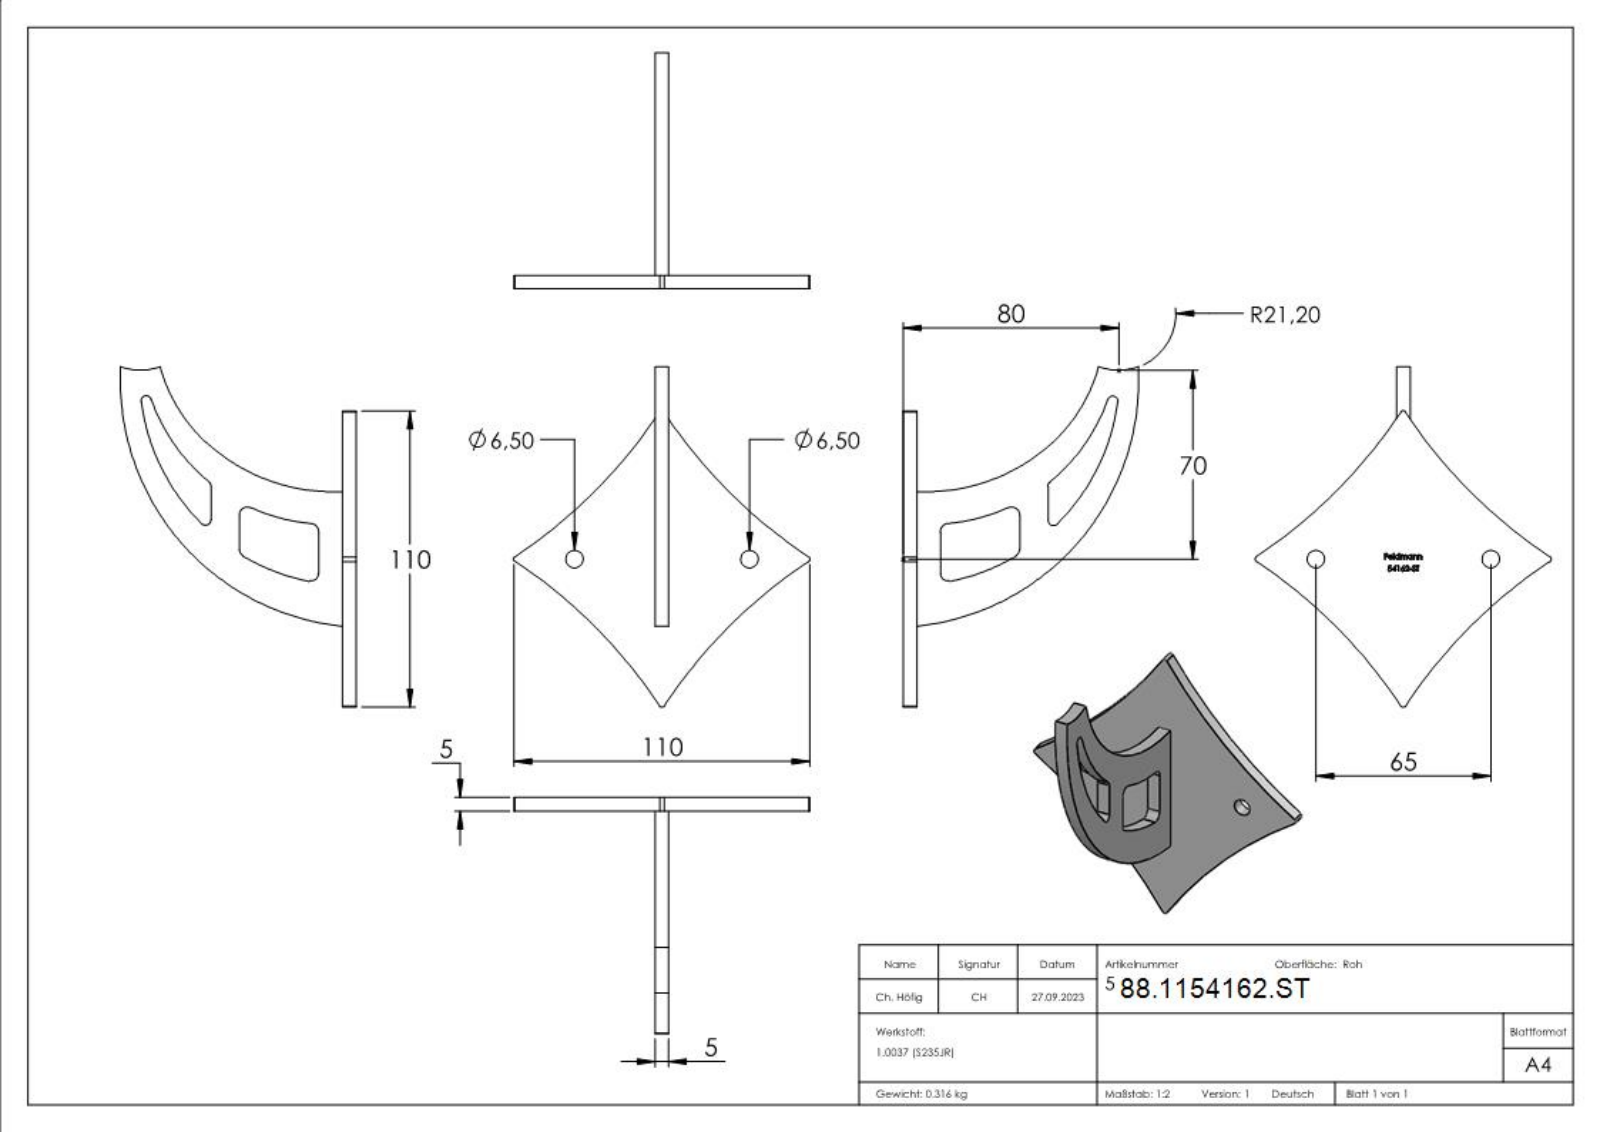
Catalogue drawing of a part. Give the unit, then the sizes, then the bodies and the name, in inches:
Units: inches
Overall size (bounding box): 4.974 × 4.331 × 3.448
Round holes (diameter × count): ⌀0.256 ×2
Partial cylindrical surfaces — rounded edges, fillets, slot ends (radius × count): R0.039 ×4, R0.079 ×2, R0.118 ×2, R7.522 ×2, R7.522 ×2, R0.075 ×1, R0.119 ×1, R0.121 ×1
Main face-to-face distances: 0.197, 0.346, 0.543, 2.117, 1.92, 1.574, 1.704, 1.507, 1.161, 0.413
Hole centre spacings: 2.559
Volume: 2.469 in³ · Surface area: 30.99 in²
Bodies: 1 solid, 241 faces (130 planar, 25 cylindrical, 86 other)
Part name (STEP PRODUCT): 54162-ST
STEP written by: SolidWorks 2018 (CONFIG_CONTROL_DESIGN)
